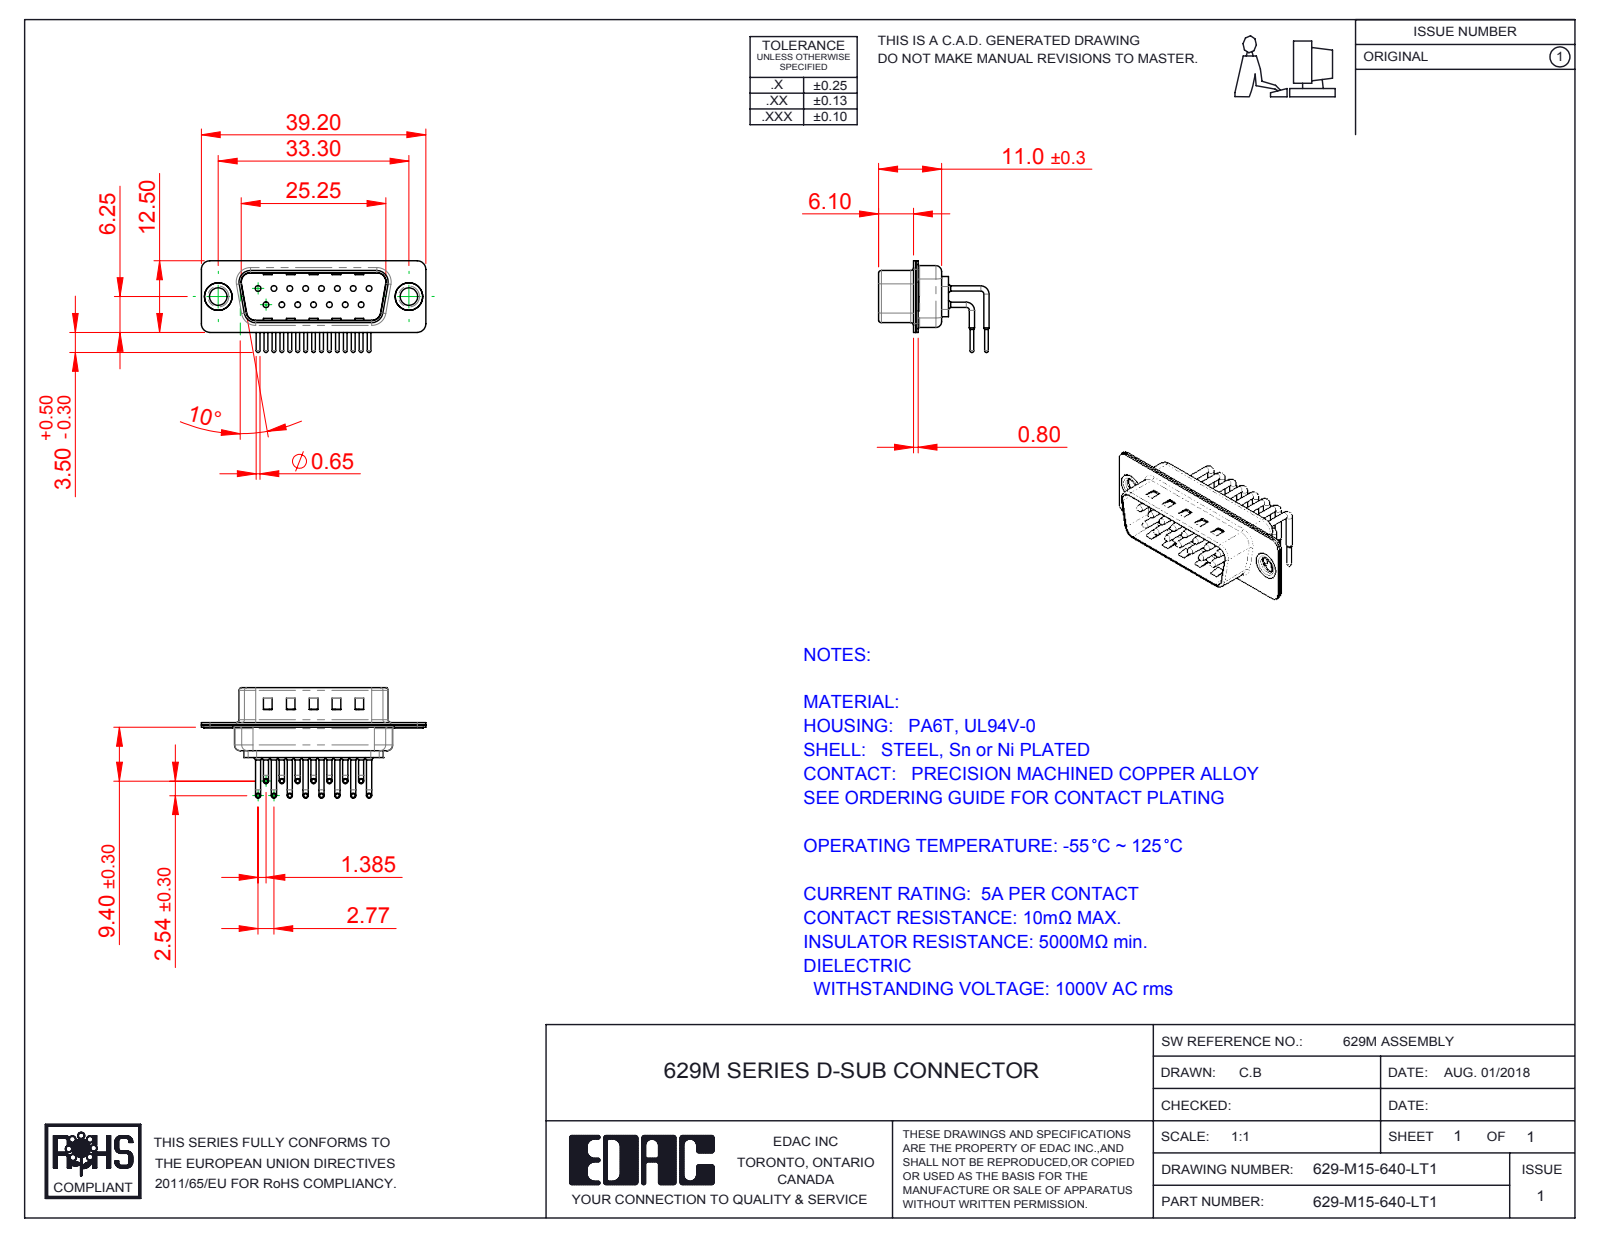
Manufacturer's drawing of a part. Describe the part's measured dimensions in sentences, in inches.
The part is named "629M Contact Row 1; 629M Contact Row 2; 629-M15-640-LT1; 629M Shell Rear_15 Contacts (+3 more)". Its 3-D file was written by "SolidWorks 2016 (CONFIG_CONTROL_DESIGN)". It is 20 solids with 1964 faces: 1099 planar, 657 cylindrical and 208 other. Overall it measures 1.543 by 0.759 by 0.63 inches. Its volume is 0.115 cubic inches and its surface area 8.08 square inches. Round holes: 15 of diameter 0.039, 15 of diameter 0.067, 15 of diameter 0.079, 2 of diameter 0.12, 2 of diameter 0.157, 2 of diameter 0.189. Round bosses or shafts: 30 of diameter 0.035, 15 of diameter 0.059, 15 of diameter 0.026, 2 of diameter 0.197, 2 of diameter 0.193, 2 of diameter 0.14. Partial cylindrical surfaces (rounded edges, fillets, slot ends): 16 of radius 0.059, 15 of radius 0.04, 12 of radius 0.079, 8 of radius 0.02, 8 of radius 0.063, 4 of radius 0.01, 4 of radius 0.024, 4 of radius 0.026. The main face-to-face distances are 0.016, 0.033, 0.376, 0.343, 0.049, 0.031, 0.409, 0.059, 0.014, 0.075. The hole center spacings are 0.124, 0.109, 0.218, 0.327, 0.436, 0.198, 0.198, 0.294.
